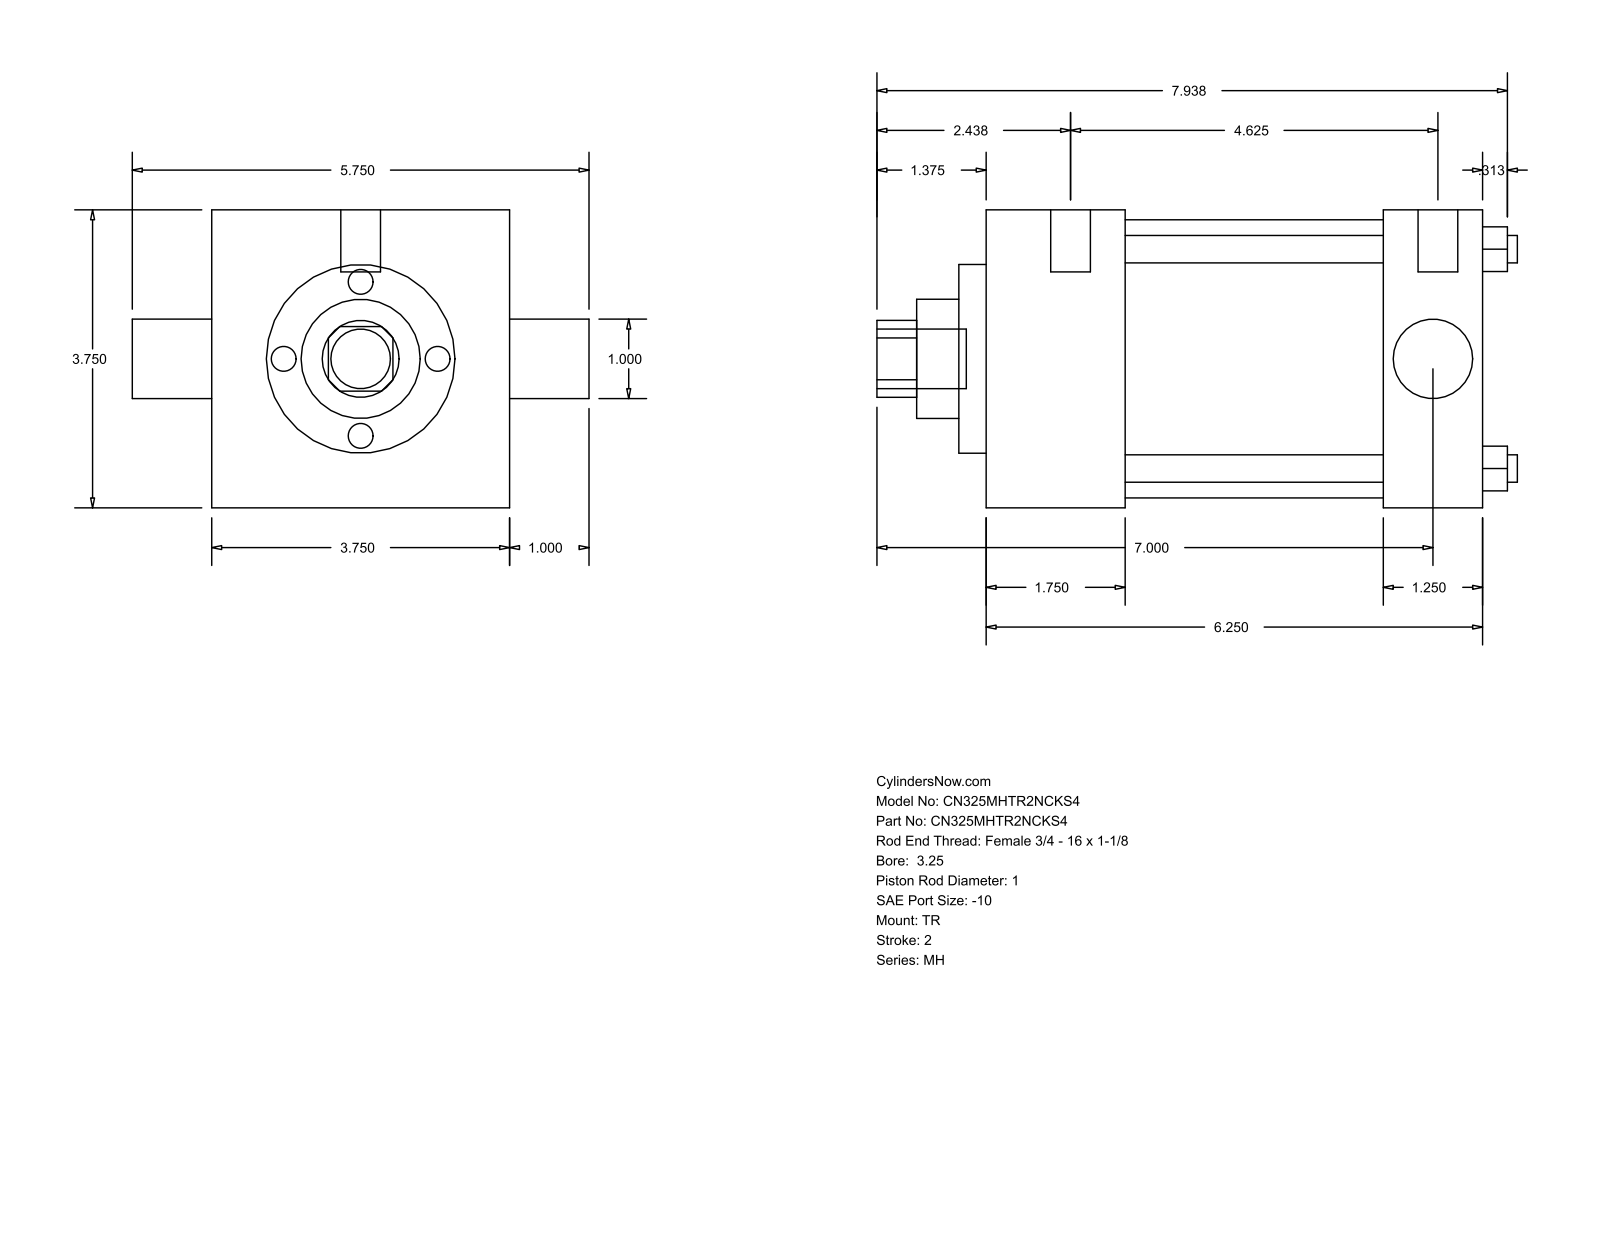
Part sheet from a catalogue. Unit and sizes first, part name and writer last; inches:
Units: inches
Overall size (bounding box): 8.063 × 5.75 × 3.75
Round holes (diameter × count): ⌀0.345 ×4, ⌀1 ×2, ⌀1.5 ×1, ⌀2.375 ×1, ⌀3.5 ×1
Round bosses / shafts (diameter × count): ⌀0.219 ×3, ⌀0.5 ×2, ⌀0.75 ×1
Partial cylindrical surfaces — rounded edges, fillets, slot ends (radius × count): R0.484 ×1
Main face-to-face distances: 3.75, 6.25, 1.75, 5, 3.25, 4.5, 1.25, 0.344, 2.094, 5.344
Hole centre spacings: 1.952, 2.76, 3.903
Bodies: 0 solids, 86 faces (61 planar, 25 cylindrical, 0 other)
Part name (STEP PRODUCT): MH_TR__0325_1
STEP written by: GSSL Pune (CONFIG_CONTROL_DESIGN)
